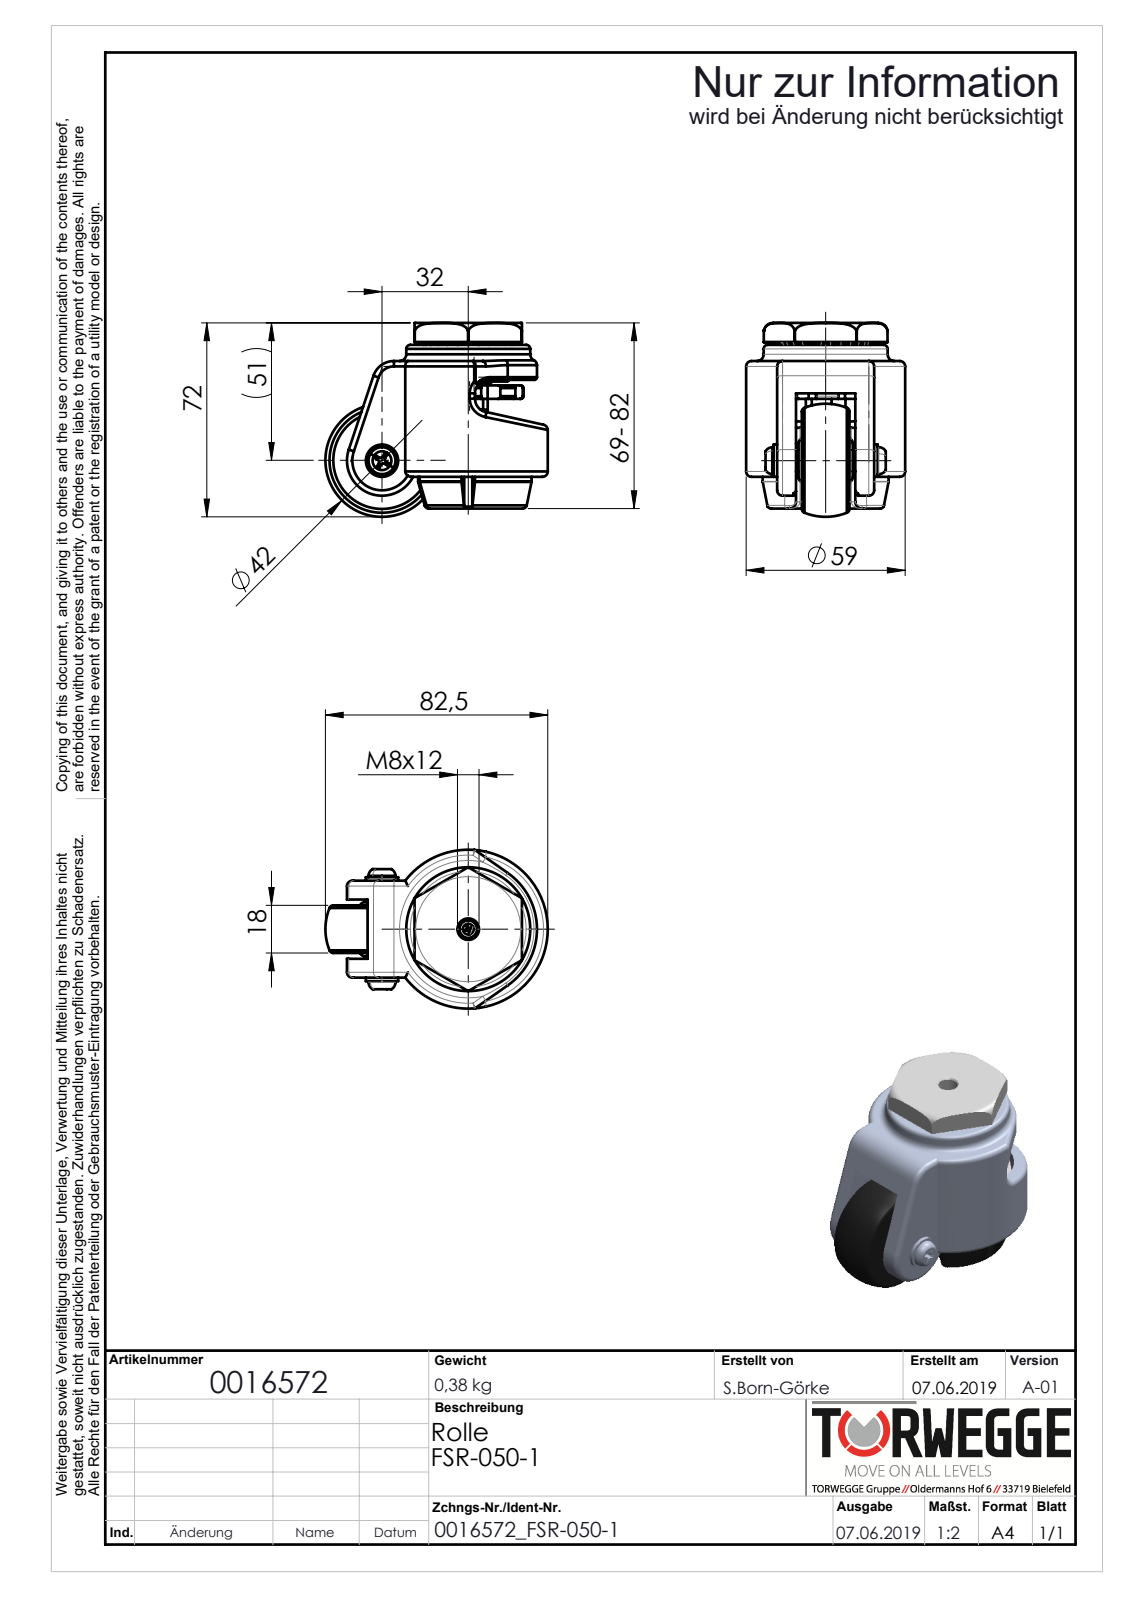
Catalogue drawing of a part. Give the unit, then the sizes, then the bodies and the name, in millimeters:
Units: millimetres
Overall size (bounding box): 80.98 × 72 × 59
Round holes (diameter × count): ⌀1.6 ×1, ⌀2 ×1, ⌀5.2 ×1, ⌀7 ×1, ⌀9 ×1, ⌀18 ×1, ⌀24 ×1, ⌀32.2 ×1
Round bosses / shafts (diameter × count): ⌀8 ×2, ⌀46 ×1, ⌀30 ×1, ⌀22.5 ×1, ⌀15 ×1, ⌀12 ×1, ⌀10 ×1, ⌀6.65 ×1
Partial cylindrical surfaces — rounded edges, fillets, slot ends (radius × count): R1 ×26, R2 ×8, R2.5 ×5, R1.5 ×2, R5 ×2, R8 ×1, R8.25 ×1, R13 ×1
Main face-to-face distances: 7, 2.15, 19.85, 29, 9.15, 26.85, 17.78, 38.93, 21.15, 30
Volume: 137 177 mm³ · Surface area: 47 712 mm²
Bodies: 8 solids, 550 faces (162 planar, 140 cylindrical, 248 other)
Part name (STEP PRODUCT): 0016572_FSR-050-1_(A-01)
STEP written by: SolidWorks 2018 (AUTOMOTIVE_DESIGN)
